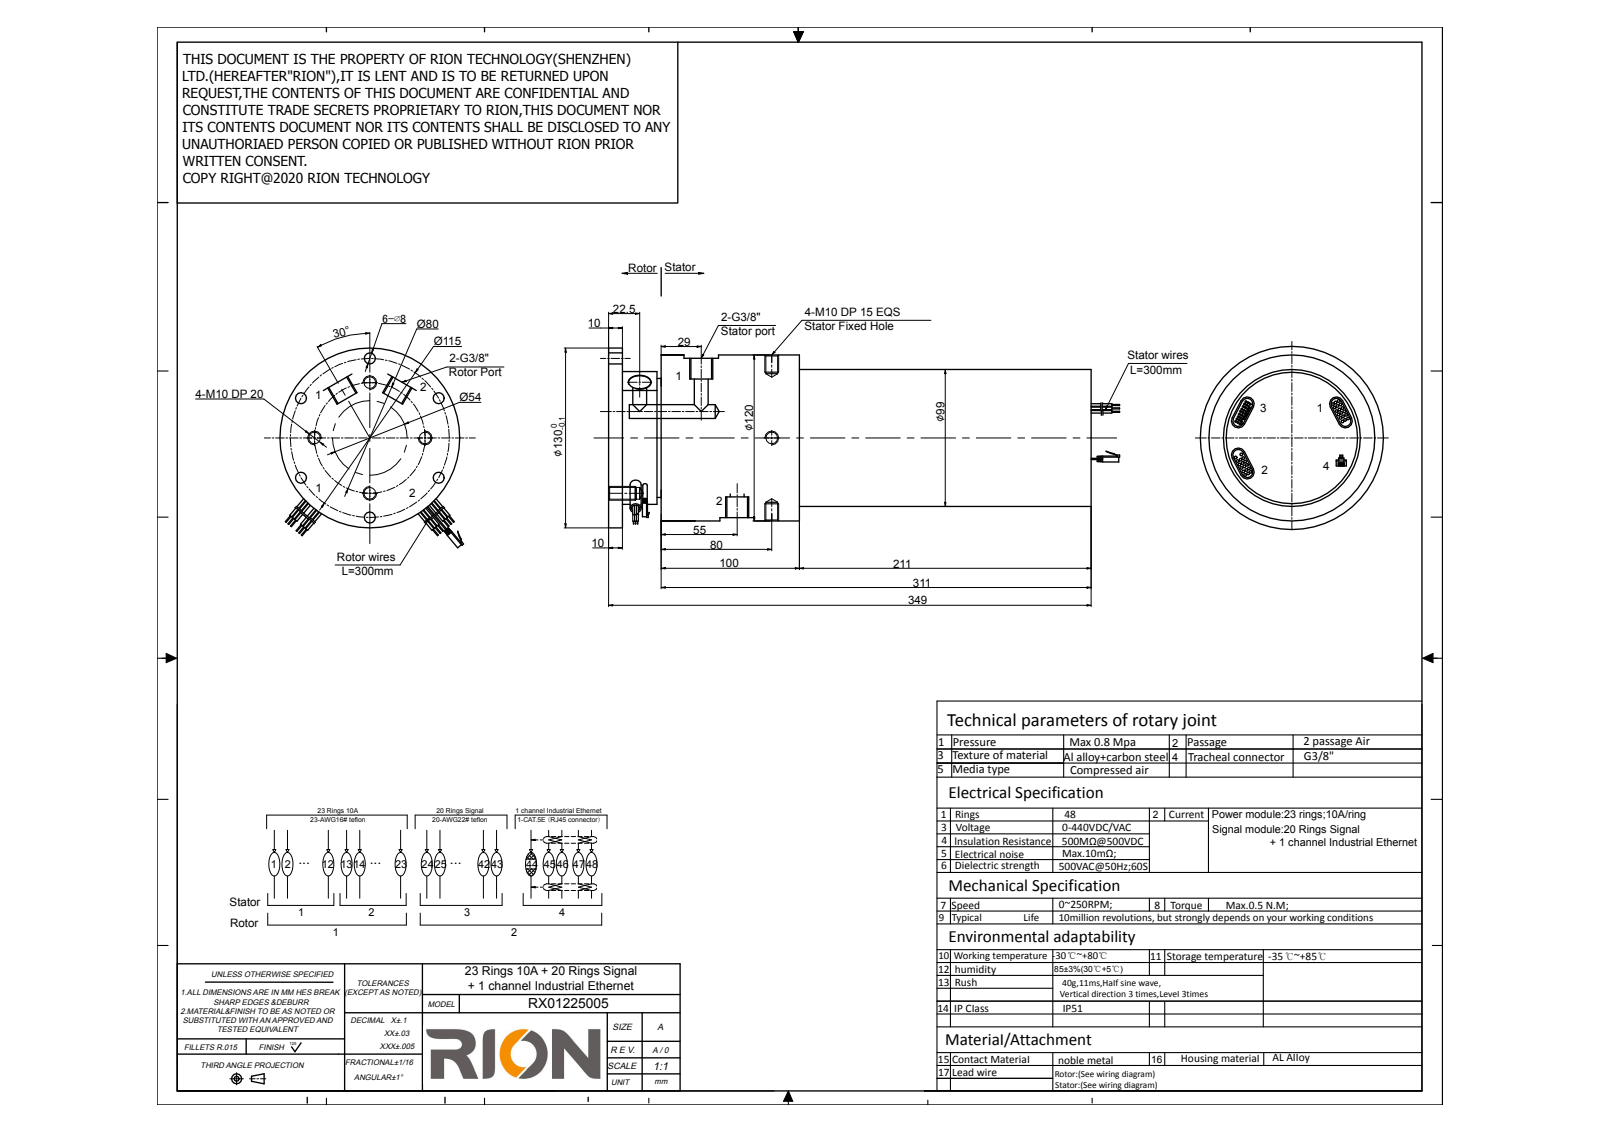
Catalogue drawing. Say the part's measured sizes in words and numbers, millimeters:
Its 3-D file was written by "SolidWorks 2014 (CONFIG_CONTROL_DESIGN)". It is 1 solid with 386 faces: 121 planar, 241 cylindrical and 24 other. Overall it measures 368.5 by 130 by 130 millimeters. Its volume is 3 057 000 cubic millimeters and its surface area 183 547 square millimeters. Round holes: 6 of diameter 8, 6 of diameter 8.5, 4 of diameter 15.25, 3 of diameter 10, 1 of diameter 95.02. Round bosses or shafts: 46 of diameter 2, 34 of diameter 1.3, 2 of diameter 6.5, 1 of diameter 130, 1 of diameter 120, 1 of diameter 99, 1 of diameter 95, 1 of diameter 81. Partial cylindrical surfaces (rounded edges, fillets, slot ends): 8 of radius 4, 4 of radius 6, 1 of radius 48. The main face-to-face distances are 349, 38, 311, 10, 28, 339, 138, 128, 100, 211. The hole center spacings are 57.5, 30.37, 40, 51.05, 56.57, 70.04, 84.89, 94.29.
